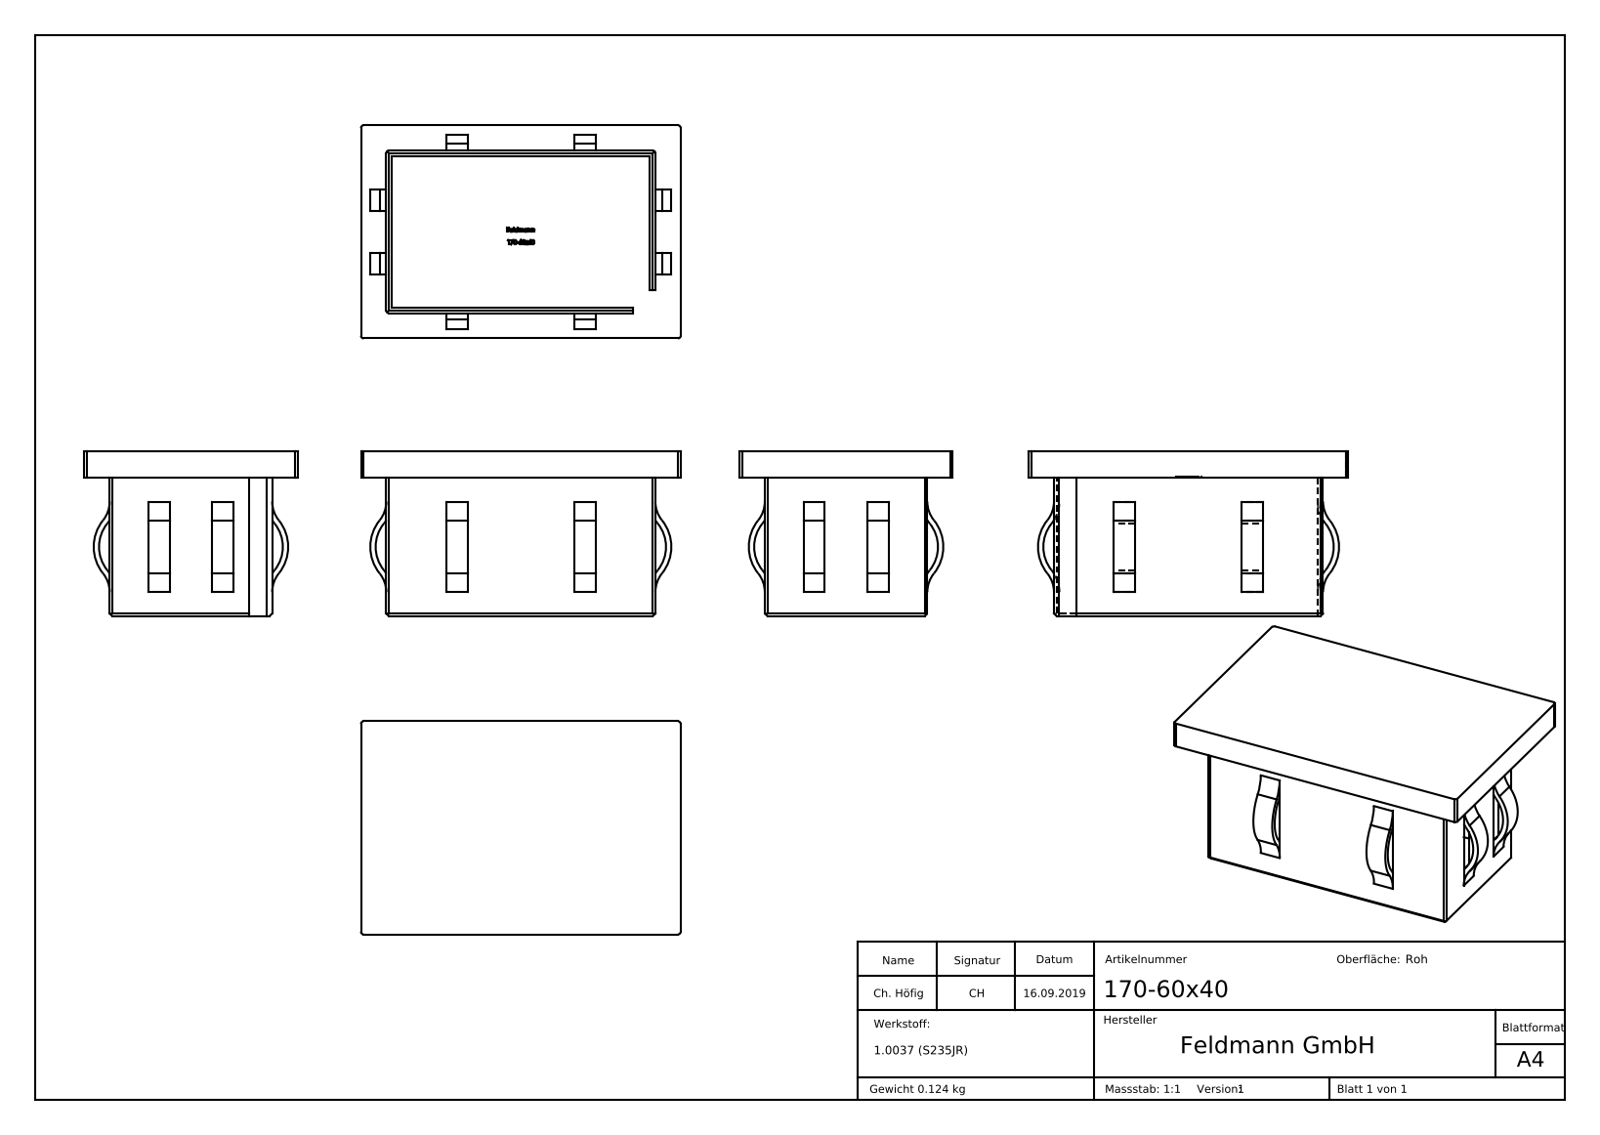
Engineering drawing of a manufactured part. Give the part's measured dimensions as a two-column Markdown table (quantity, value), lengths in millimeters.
| quantity | value |
| --- | --- |
| part name | 170-60x40 |
| STEP written by | SolidWorks 2015 (CONFIG_CONTROL_DESIGN) |
| units | millimeters |
| bodies | 1 solid, 366 faces (189 planar, 63 cylindrical, 114 other) |
| overall size | 60 × 40 × 31 |
| volume | 15 933 mm³ |
| surface area | 14 121 mm² |
| partial cylindrical surfaces (radius × count) | 5.58 × 8, 6.58 × 8, 0.5 × 7, 6.97 × 4, 7.97 × 4 |
| main face-to-face distances | 1, 5, 29.5, 49.5, 28.5, 30.5, 4.75, 5.75, 34.25, 35.25 |
